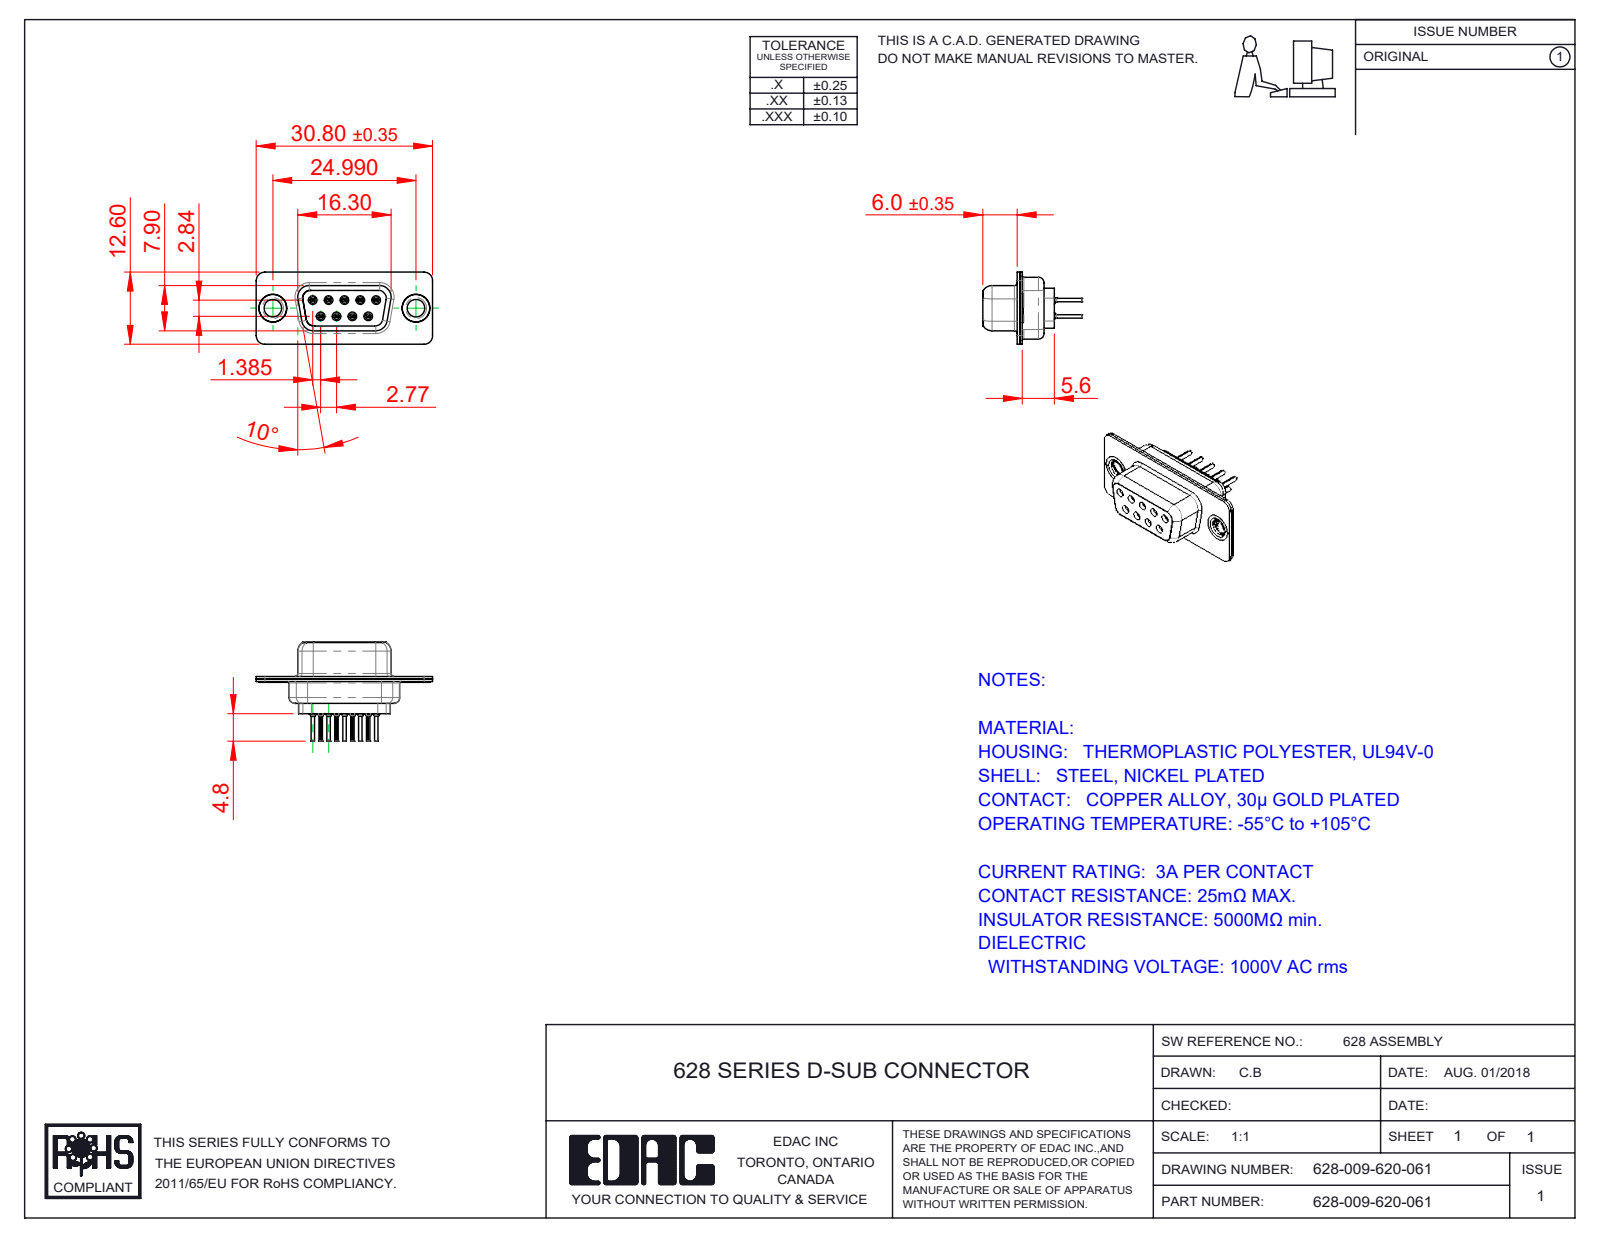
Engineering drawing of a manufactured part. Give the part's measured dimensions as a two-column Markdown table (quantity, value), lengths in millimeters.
| quantity | value |
| --- | --- |
| part name | 628 Contact Row 2_20L; 628-009-620-061; 628 Housing_09 LP; 628 Thru Hole Rivet (+3 more) |
| STEP written by | SolidWorks 2020 (CONFIG_CONTROL_DESIGN) |
| units | millimeters |
| bodies | 14 solids, 1396 faces (346 planar, 418 cylindrical, 632 other) |
| overall size | 30.8 × 17.3 × 12.6 |
| volume | 1 681 mm³ |
| surface area | 4 363 mm² |
| round holes (diameter × count) | 0.2 × 9, 0.8 × 9, 0.9 × 9, 1.1 × 9, 1.6 × 9, 1.7 × 5, 3.05 × 2, 4 × 2, 4.05 × 2, 4.85 × 2 |
| round bosses / shafts (diameter × count) | 2 × 9, 1.5 × 9, 1.2 × 9, 0.6 × 9, 5 × 2, 4.95 × 2, 4.8 × 2, 3.55 × 2 |
| partial cylindrical surfaces (radius × count) | 0.1 × 18, 1.5 × 17, 2 × 12, 0.28 × 9, 1.35 × 6, 0.25 × 4, 0.5 × 4, 0.6 × 4 |
| main face-to-face distances | 0.45, 0.4, 0.9, 1.9, 8.5, 6.6, 1.4, 7.05, 0.5, 1.05 |
| hole center spacings | 3.16, 2.77, 5.54, 5.03, 5.04, 8.31, 7.48, 7.49 |
